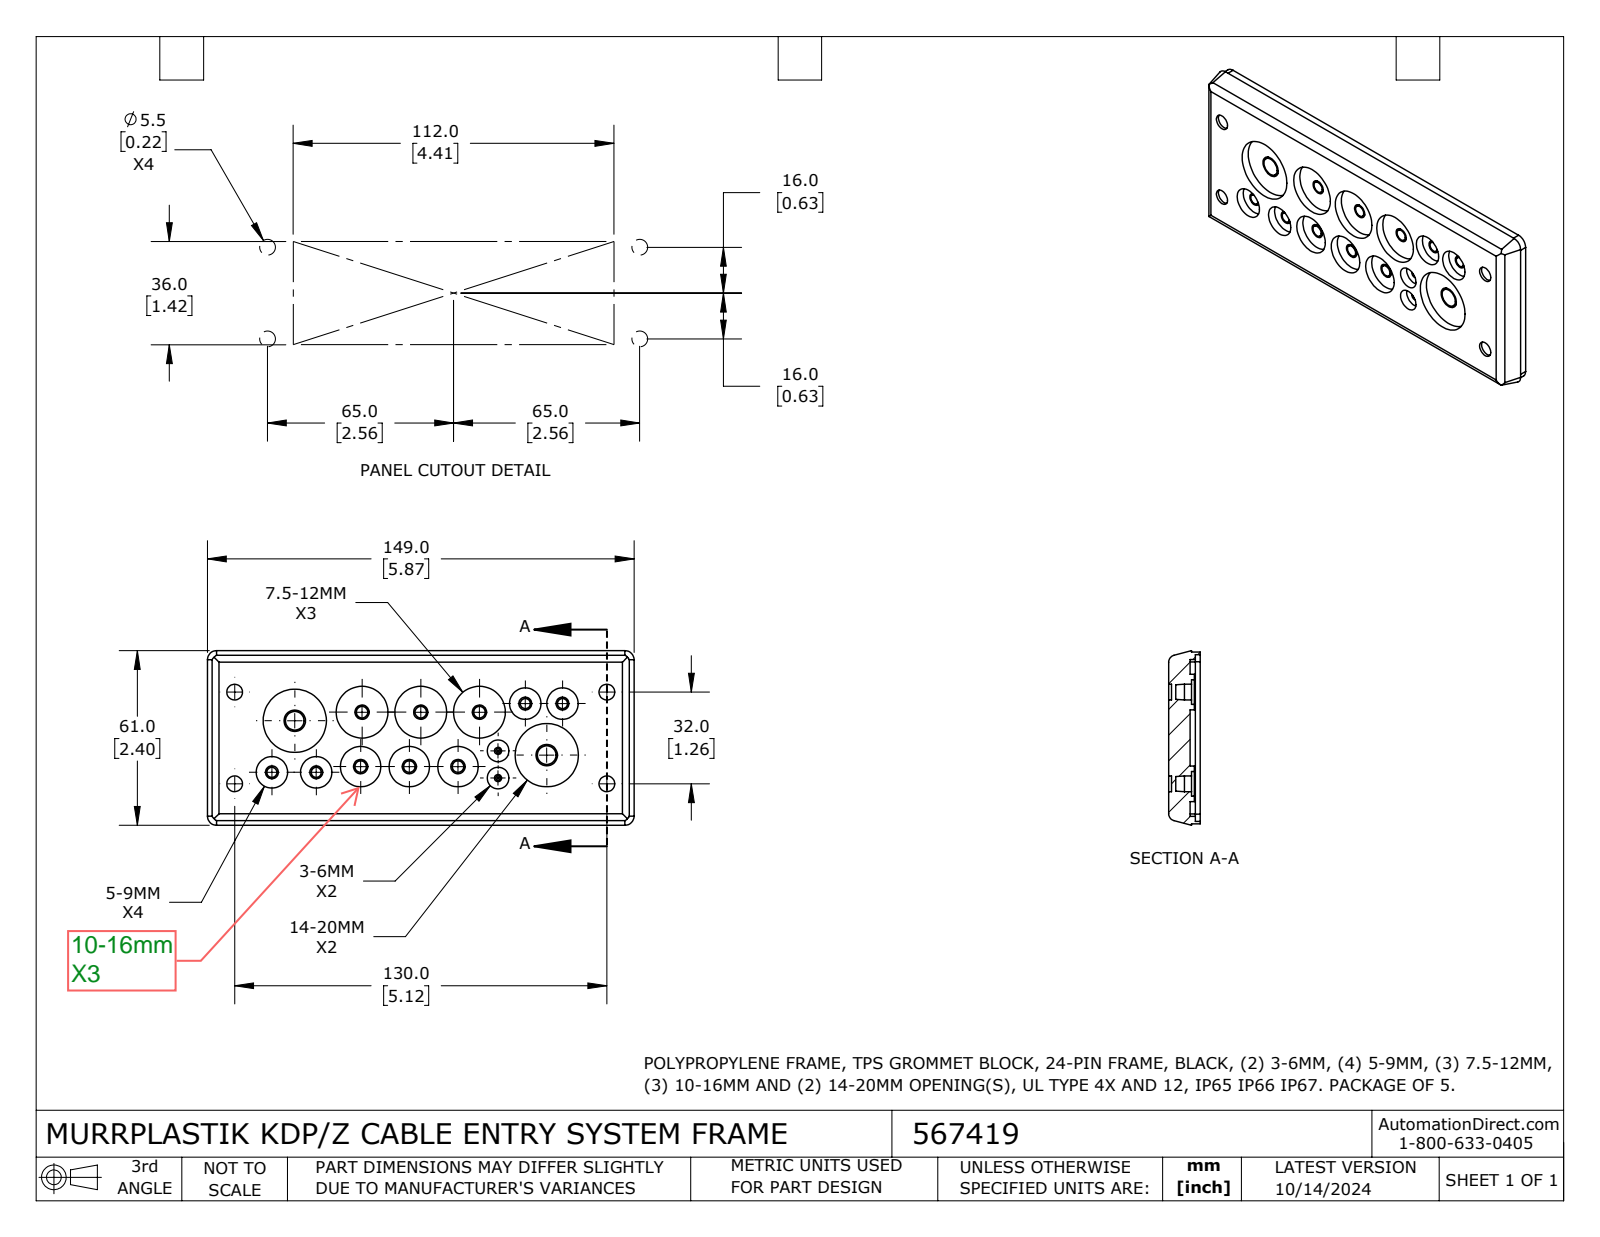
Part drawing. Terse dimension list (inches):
name: 567419
written by: SolidWorks 2023 (CONFIG_CONTROL_DESIGN)
unit: in
bodies: 1 solid, 259 faces (93 planar, 154 cylindrical, 12 other)
size: 5.866 × 2.402 × 0.433
volume: 2.865 in³; area: 44.67 in²
holes: 6× ⌀0.197, 4× ⌀0.177, 4× ⌀0.217, 4× ⌀0.339, 3× ⌀0.432, 3× ⌀0.712, 2× ⌀0.098, 2× ⌀0.295, 2× ⌀0.299, 2× ⌀0.554, 2× ⌀0.869, 1× ⌀0.432
bosses: 6× ⌀0.157, 4× ⌀0.488, 4× ⌀0.138, 2× ⌀0.256, 2× ⌀0.059
rounds: 16× R0.012, 4× R0.035, 4× R0.098, 4× R0.098, 4× R0.138, 4× R0.305
face distances: 0.217, 0.098, 0.118, 0.079, 0.177, 0.295, 0.067, 0.433, 0.347, 2.015
hole spacings: 1.26, 0.669, 0.768, 0.807, 0.916, 1.133, 1.197, 1.231
